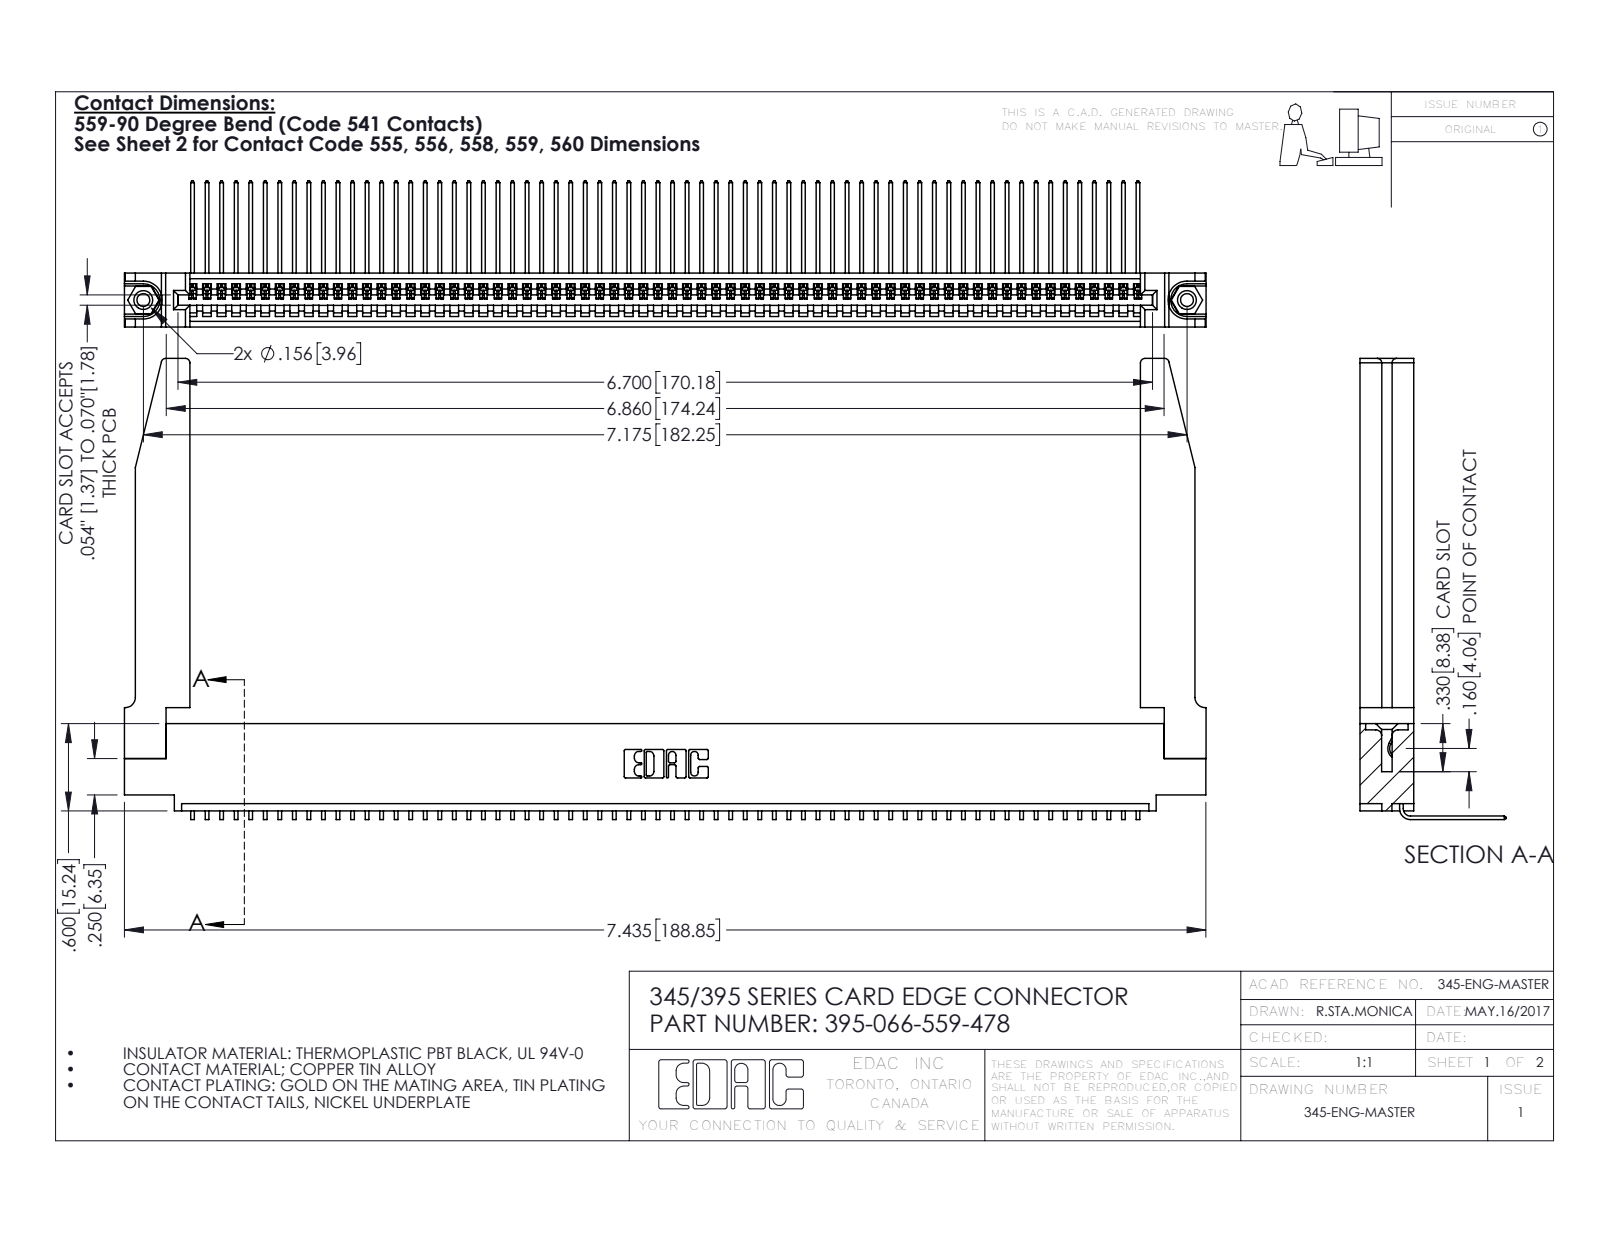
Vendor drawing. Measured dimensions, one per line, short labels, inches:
name: 345 Part_0.110 Offset - 0.156 Dia-TH; 345-250-001_345-250-001-102; 345-220-078_345-220-078; 345-292-001_558 559 Tail - 1 (+1 more)
written by: SolidWorks 2016 (CONFIG_CONTROL_DESIGN)
unit: in
bodies: 71 solids, 4324 faces (2998 planar, 1274 cylindrical, 52 other)
size: 7.436 × 3.169 × 1.005
volume: 1.59 in³; area: 50.9 in²
holes: 2× ⌀0.089, 2× ⌀0.125, 2× ⌀0.156, 1× ⌀0.064
bosses: 2× ⌀0.155
rounds: 132× R0.006, 22× R0.01, 8× R0.03, 6× R0.007, 6× R0.031, 3× R0.026, 2× R0.031, 2× R0.04
face distances: 0.37, 0.072, 0.298, 0.098, 0.272, 0.025, 0.2, 0.225, 0.15, 0.148
hole spacings: 0.27, 6.939, 7.175
